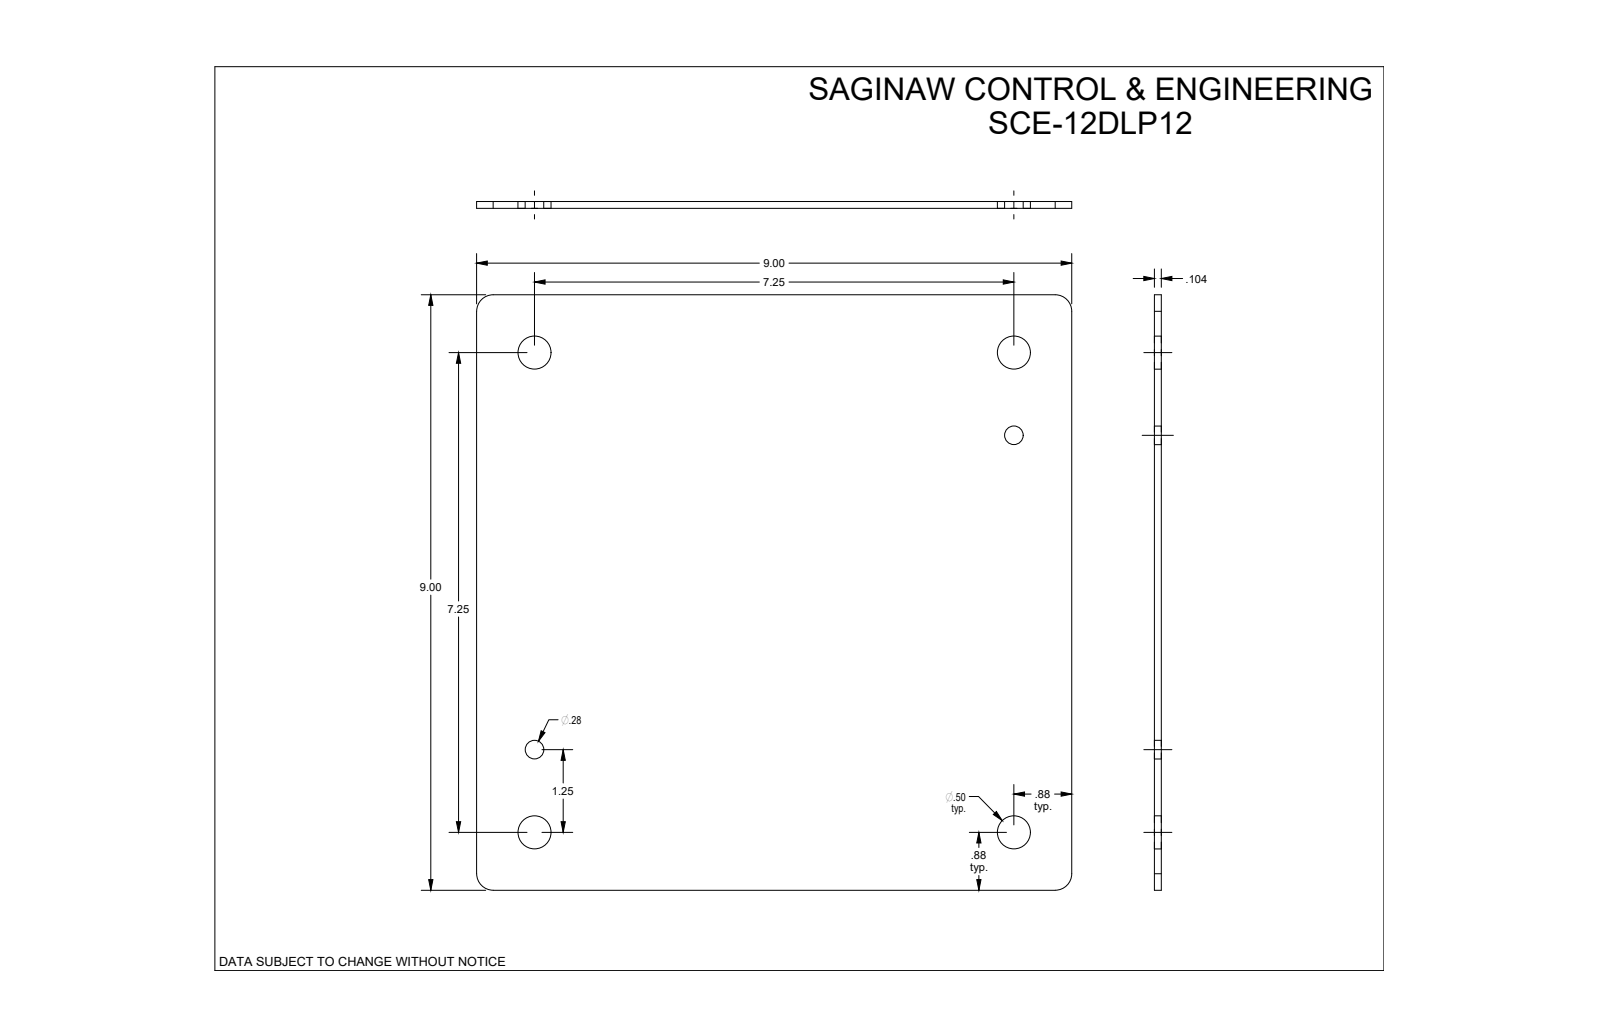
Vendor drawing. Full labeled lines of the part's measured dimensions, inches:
Part name (STEP PRODUCT): SCE-12DLP12
STEP written by: SolidWorks 2019 (CONFIG_CONTROL_DESIGN)
Units: inches
Bodies: 1 solid, 16 faces (6 planar, 10 cylindrical, 0 other)
Overall size (bounding box): 9 × 9 × 0.104
Volume: 8.324 in³ · Surface area: 164.6 in²
Round holes (diameter × count): ⌀0.5 ×4, ⌀0.281 ×1, ⌀0.281 ×1
Partial cylindrical surfaces — rounded edges, fillets, slot ends (radius × count): R0.25 ×4
Main face-to-face distances: 0.104, 9
Hole centre spacings: 7.25, 1.25, 6, 7.357, 9.41, 10.252, 8.667
